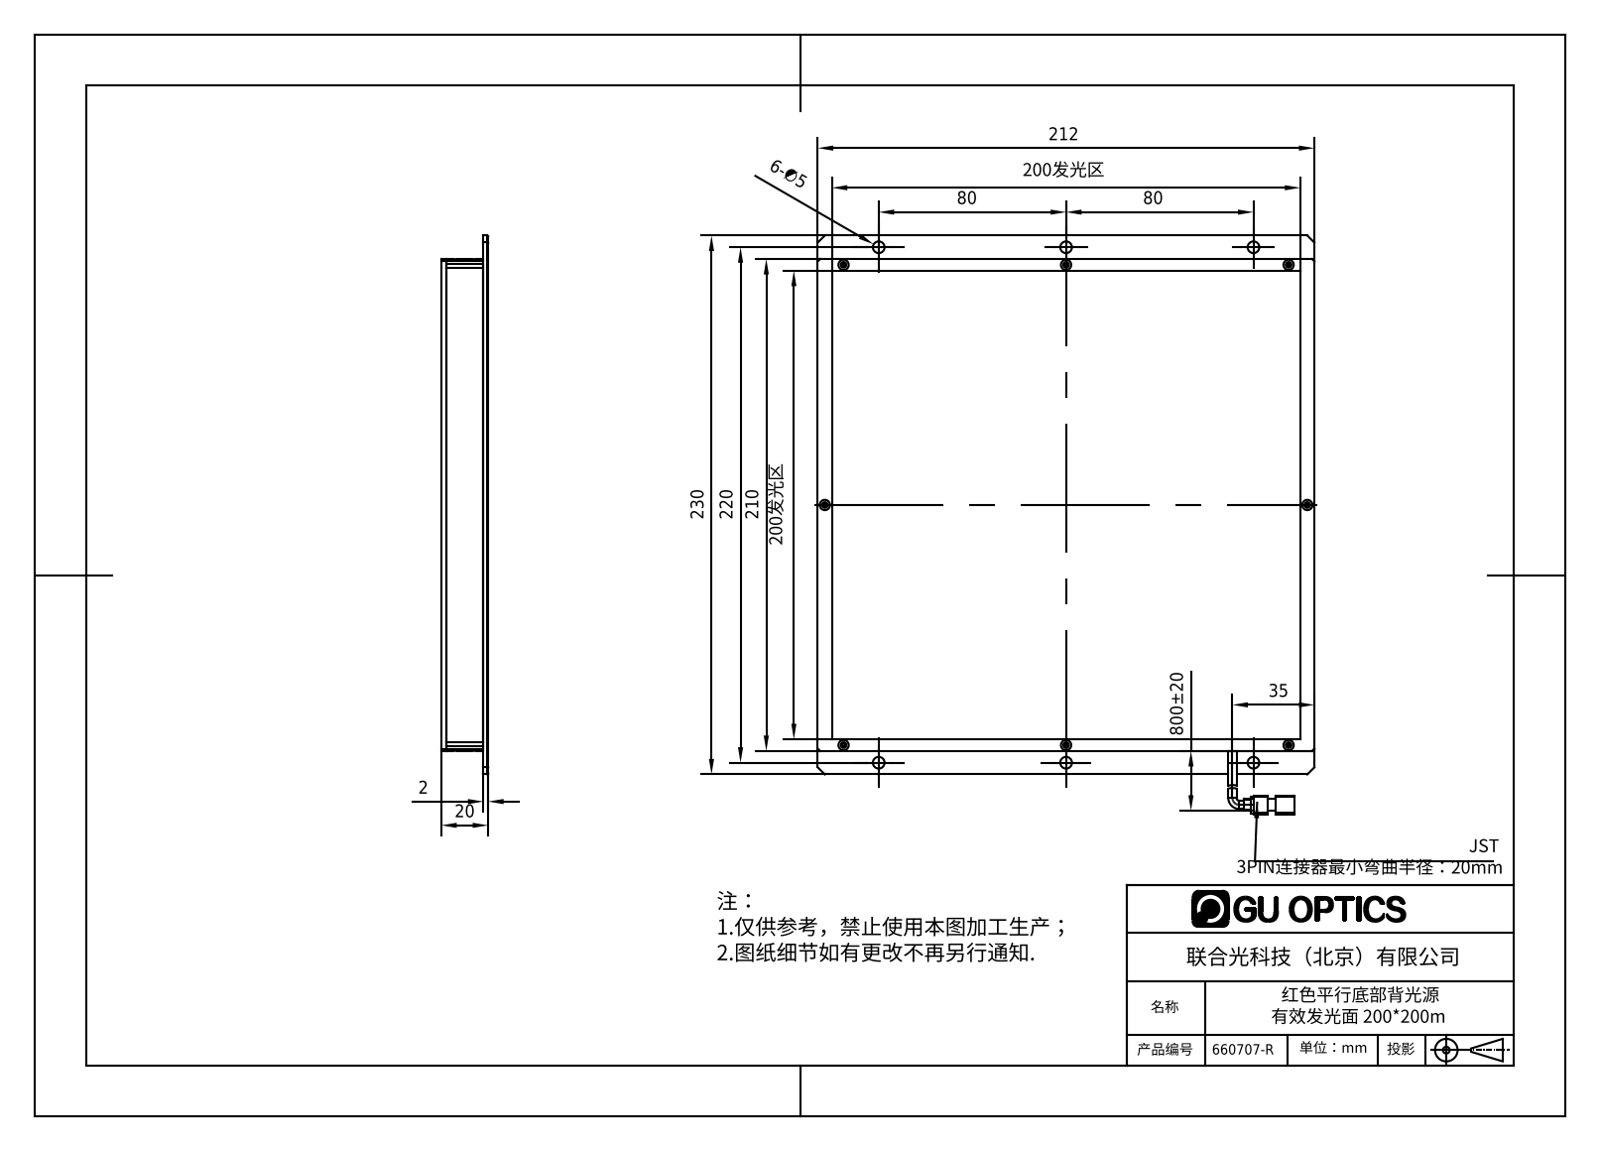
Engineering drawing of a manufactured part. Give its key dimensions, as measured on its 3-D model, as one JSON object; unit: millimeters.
{"part_name": "660707-R", "step_written_by": "SolidWorks 2016 (AUTOMOTIVE_DESIGN)", "units": "millimeters", "bodies": {"solids": 8, "faces": 520, "planar": 197, "cylindrical": 149, "other": 174}, "overall_size": [247, 212, 22.4], "volume_mm3": 261476, "surface_area_mm2": 228305, "round_holes": [[1.6, 16], [2.4, 16], [5, 6]], "round_bosses_or_shafts": [[3.5, 2]], "partial_cylinders_radius": [[0.5, 8], [1, 4], [2, 2], [1.6, 1]], "face_to_face_distances": [2, 18, 16, 2.1, 20.1, 18.1, 6, 206, 5, 200], "hole_center_spacings": [95, 206, 10.97, 16.77, 27.46, 80, 80.35, 95.3]}
